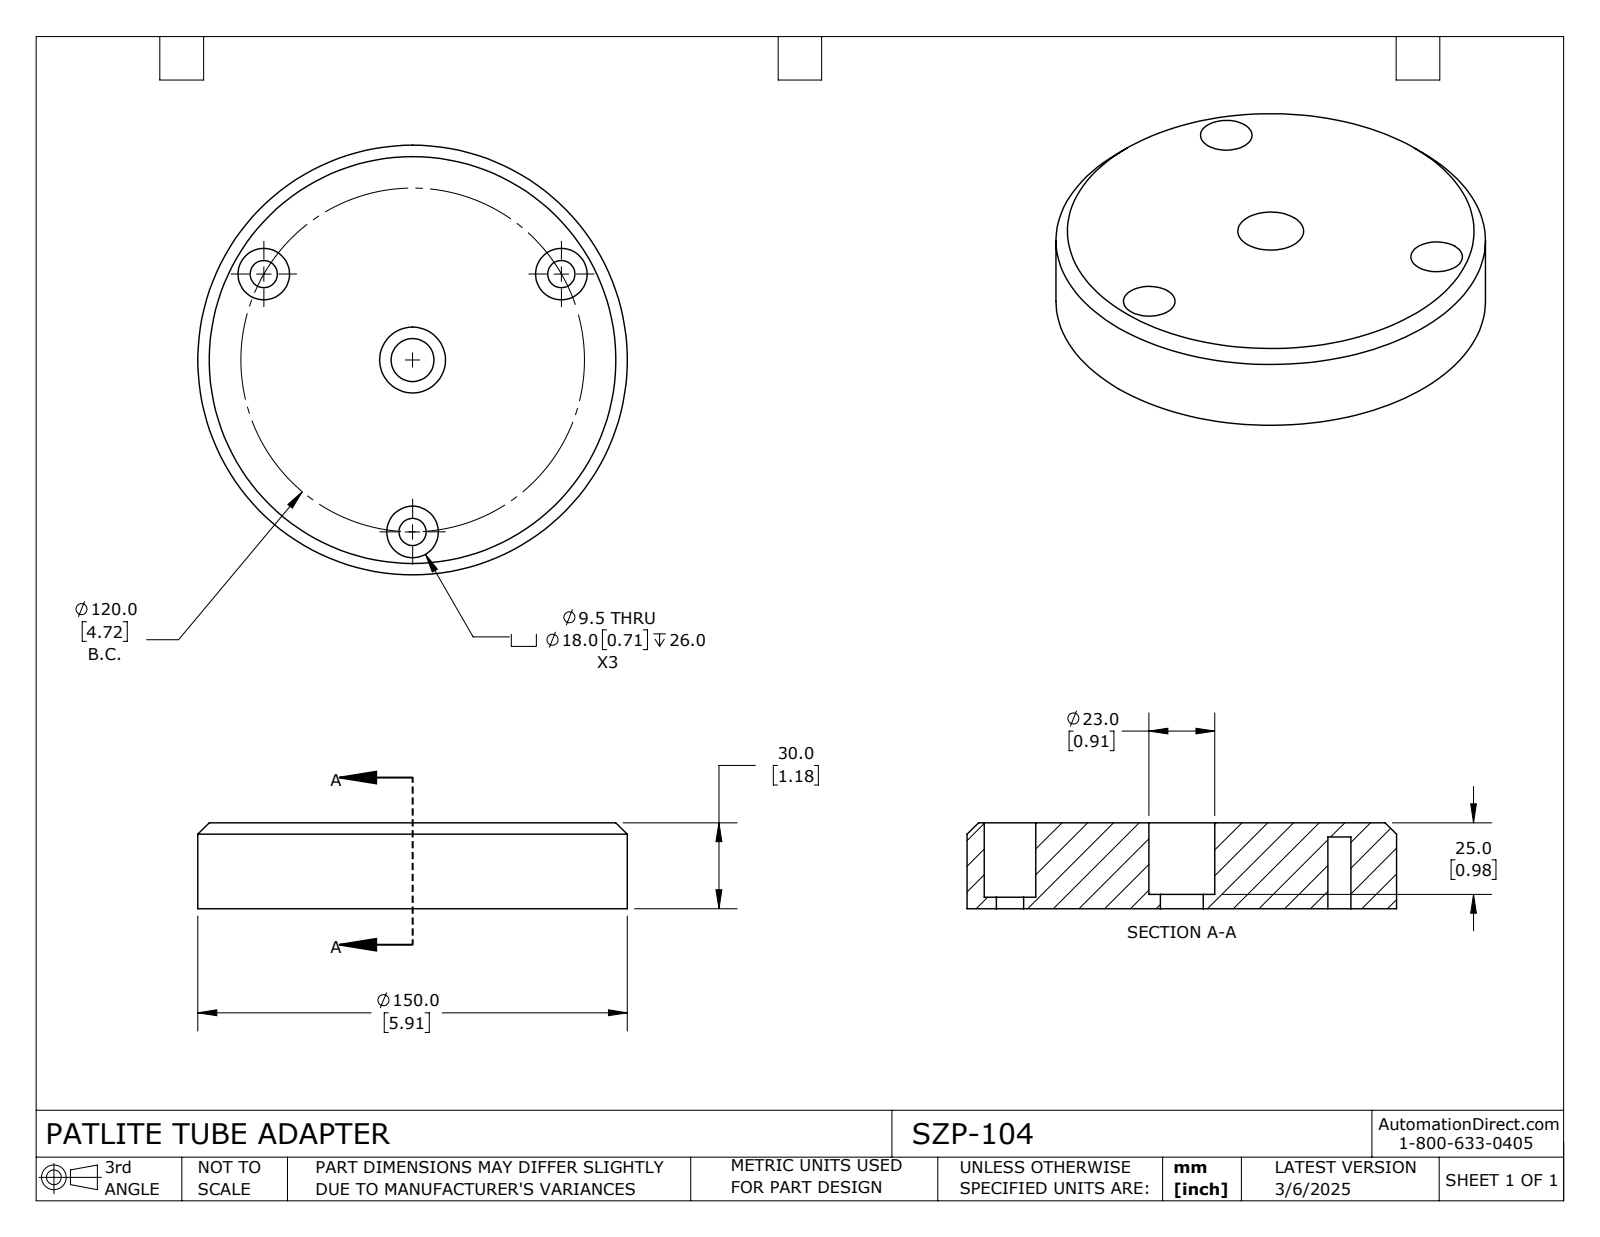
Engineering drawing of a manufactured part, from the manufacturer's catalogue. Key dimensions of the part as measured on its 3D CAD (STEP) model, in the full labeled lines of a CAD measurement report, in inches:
Part name (STEP PRODUCT): SZP-104
STEP written by: SolidWorks 2024 (CONFIG_CONTROL_DESIGN)
Units: inches
Bodies: 1 solid, 35 faces (9 planar, 24 cylindrical, 2 other)
Overall size (bounding box): 5.906 × 5.906 × 1.181
Volume: 29.94 in³ · Surface area: 87.24 in²
Round holes (diameter × count): ⌀0.317 ×3, ⌀0.374 ×3, ⌀0.709 ×3, ⌀0.591 ×1, ⌀0.906 ×1
Round bosses / shafts (diameter × count): ⌀5.906 ×1
Main face-to-face distances: 1.181, 0.157, 1.024, 0.197, 0.984, 0.039, 0.827, 0.787
Hole centre spacings: 2.27, 2.165, 2.362, 3.75, 4.091, 4.528
